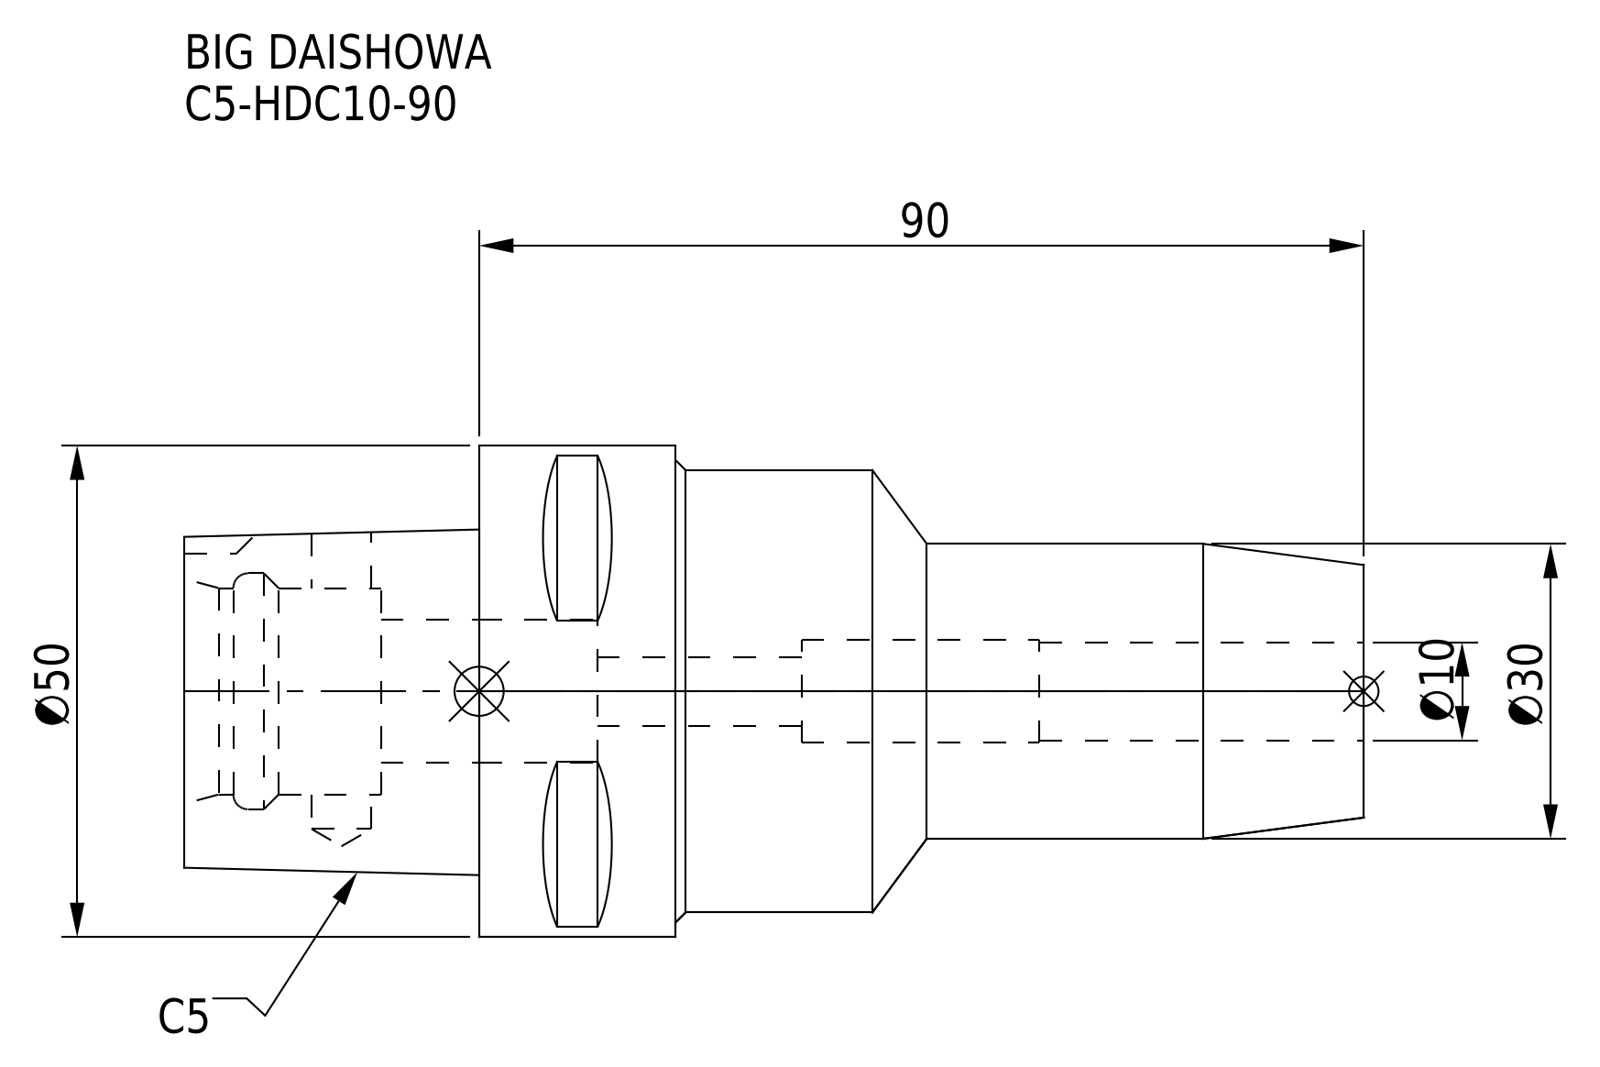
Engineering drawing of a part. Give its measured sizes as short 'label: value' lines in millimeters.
name: C5-HDC10-90
written by: CREO PARAMETRIC BY PTC INC, 2016380 (AUTOMOTIVE_DESIGN)
unit: mm
bodies: 1 solid, 71 faces (30 planar, 25 cylindrical, 16 other)
size: 120 × 50 × 50
volume: 116 926 mm³; area: 22 071 mm²
holes: 1× ⌀6.1, 1× ⌀7, 1× ⌀10, 1× ⌀10.5, 1× ⌀14.5, 1× ⌀21, 1× ⌀24
bosses: 1× ⌀50, 1× ⌀45, 1× ⌀30
rounds: 1× R4
face distances: 30, 90, 20, 120, 70, 50, 44, 100, 10, 19.18
